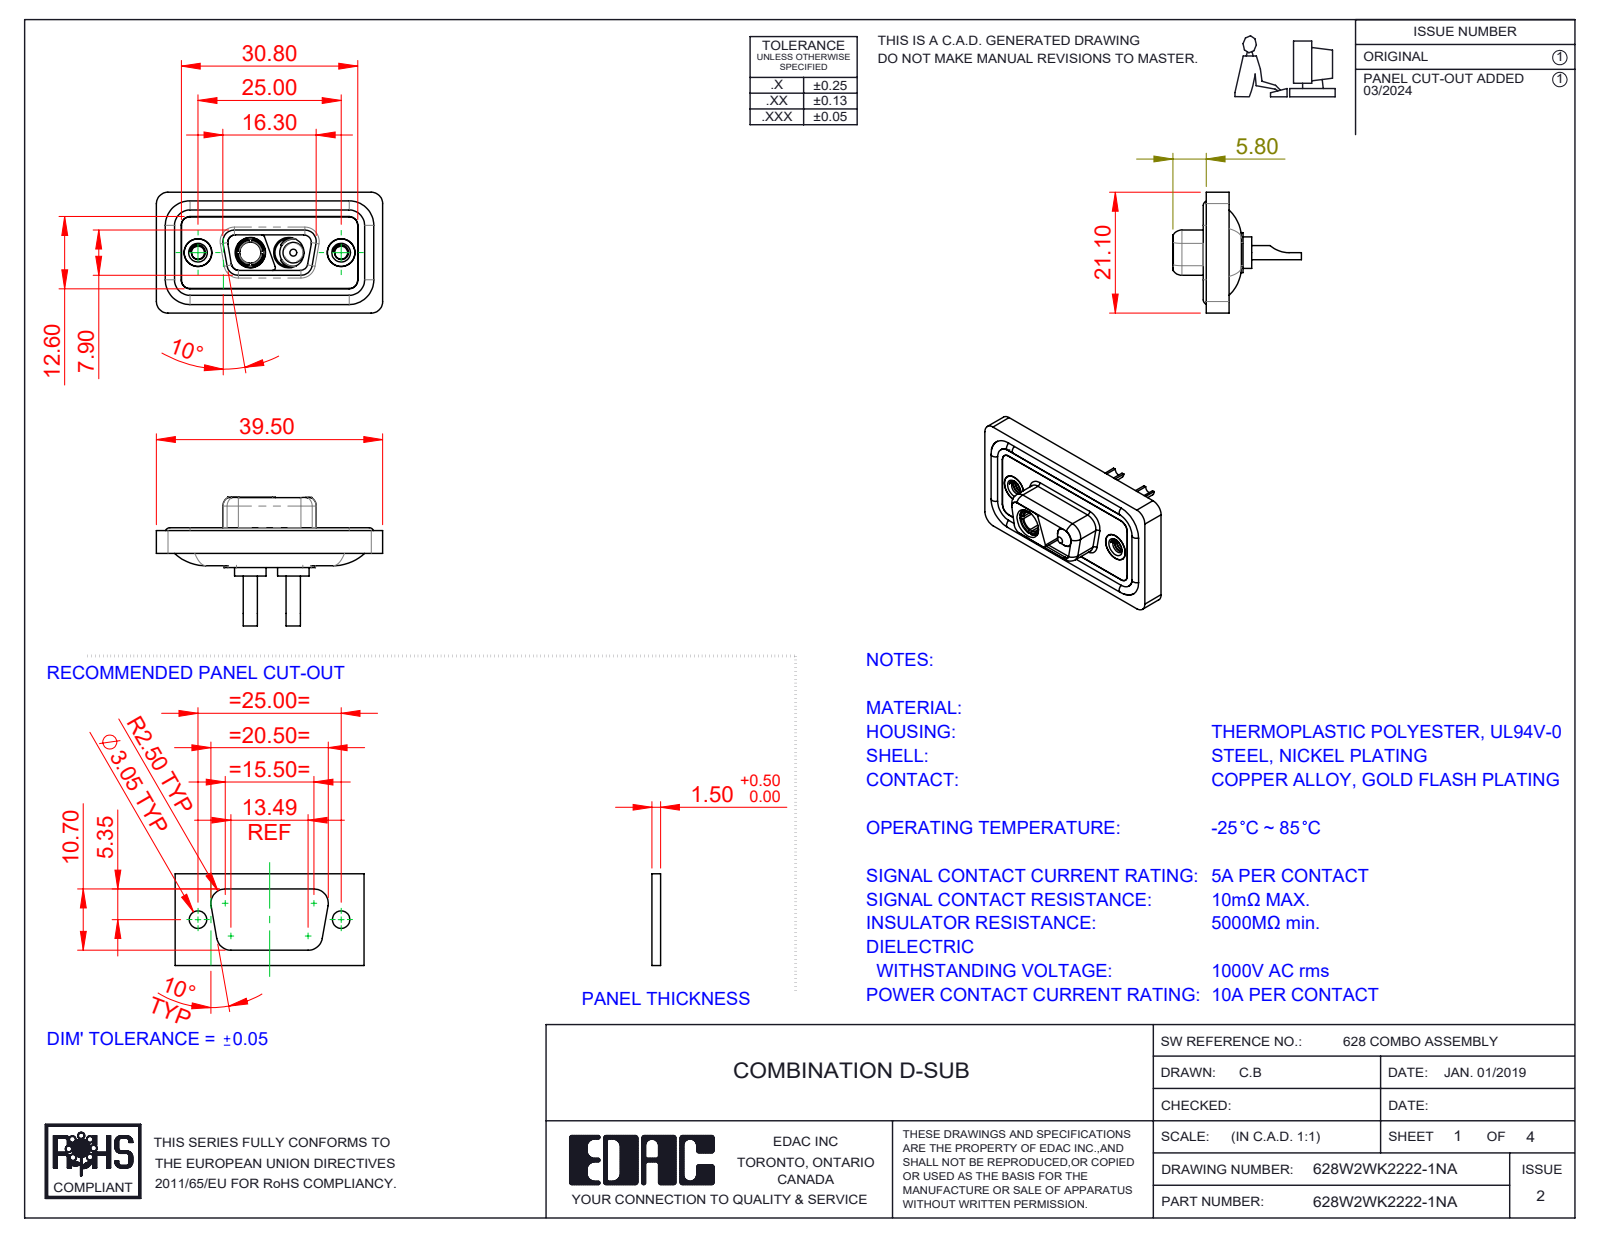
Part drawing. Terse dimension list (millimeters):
name: 628W2WK2222-1NA; Power Socket_10A SC; 628Combo Threaded Rivet_A; 628Combo Waterproof Housing_09 Contacts (+4 more)
written by: SolidWorks 2023 (CONFIG_CONTROL_DESIGN)
unit: mm
bodies: 11 solids, 508 faces (148 planar, 239 cylindrical, 121 other)
size: 39.5 × 22.45 × 21.1
volume: 4 599 mm³; area: 7 437 mm²
holes: 4× ⌀4.85, 2× ⌀1.7, 2× ⌀2.26, 2× ⌀4, 2× ⌀4.05, 2× ⌀5, 2× ⌀5.3, 1× ⌀3.7
bosses: 4× ⌀1.6, 2× ⌀5.5, 2× ⌀5.2, 2× ⌀4.95, 2× ⌀4.8, 2× ⌀4.75, 2× ⌀3.75, 2× ⌀2.5
rounds: 22× R1.5, 18× R2, 8× R1.35, 8× R1.6, 6× R0.5, 4× R0.25, 4× R0.6, 4× R0.65
face distances: 0.4, 1.1, 2.9, 1.6, 0.5, 1.8, 5.65, 1.5, 5.35, 3.1
hole spacings: 9.14, 15.86, 6.72, 25
